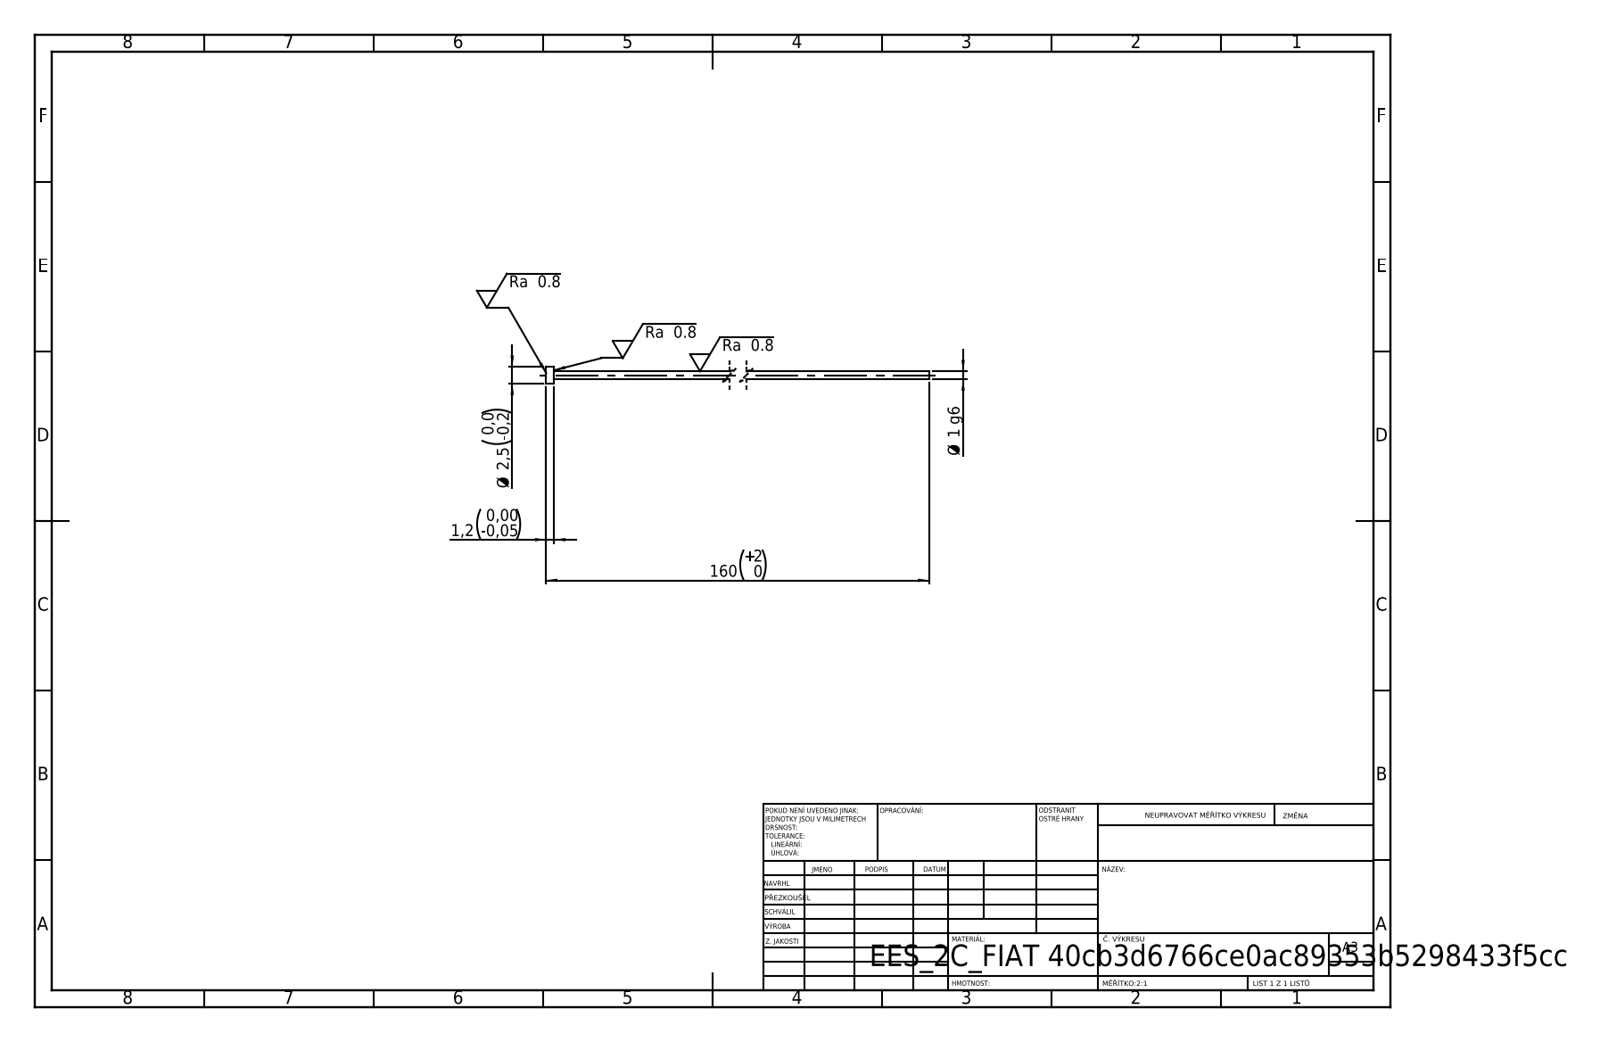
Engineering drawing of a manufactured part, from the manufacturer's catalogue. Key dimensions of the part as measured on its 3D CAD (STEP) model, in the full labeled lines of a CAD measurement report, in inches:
STEP written by: SolidWorks 2019 (CONFIG_CONTROL_DESIGN)
Units: inches
Bodies: 1 solid, 7 faces (3 planar, 4 cylindrical, 0 other)
Overall size (bounding box): 6.299 × 0.098 × 0.098
Volume: 0.011 in³ · Surface area: 0.958 in²
Round bosses / shafts (diameter × count): ⌀0.098 ×1, ⌀0.047 ×1
Main face-to-face distances: 0.047, 6.299, 6.252
